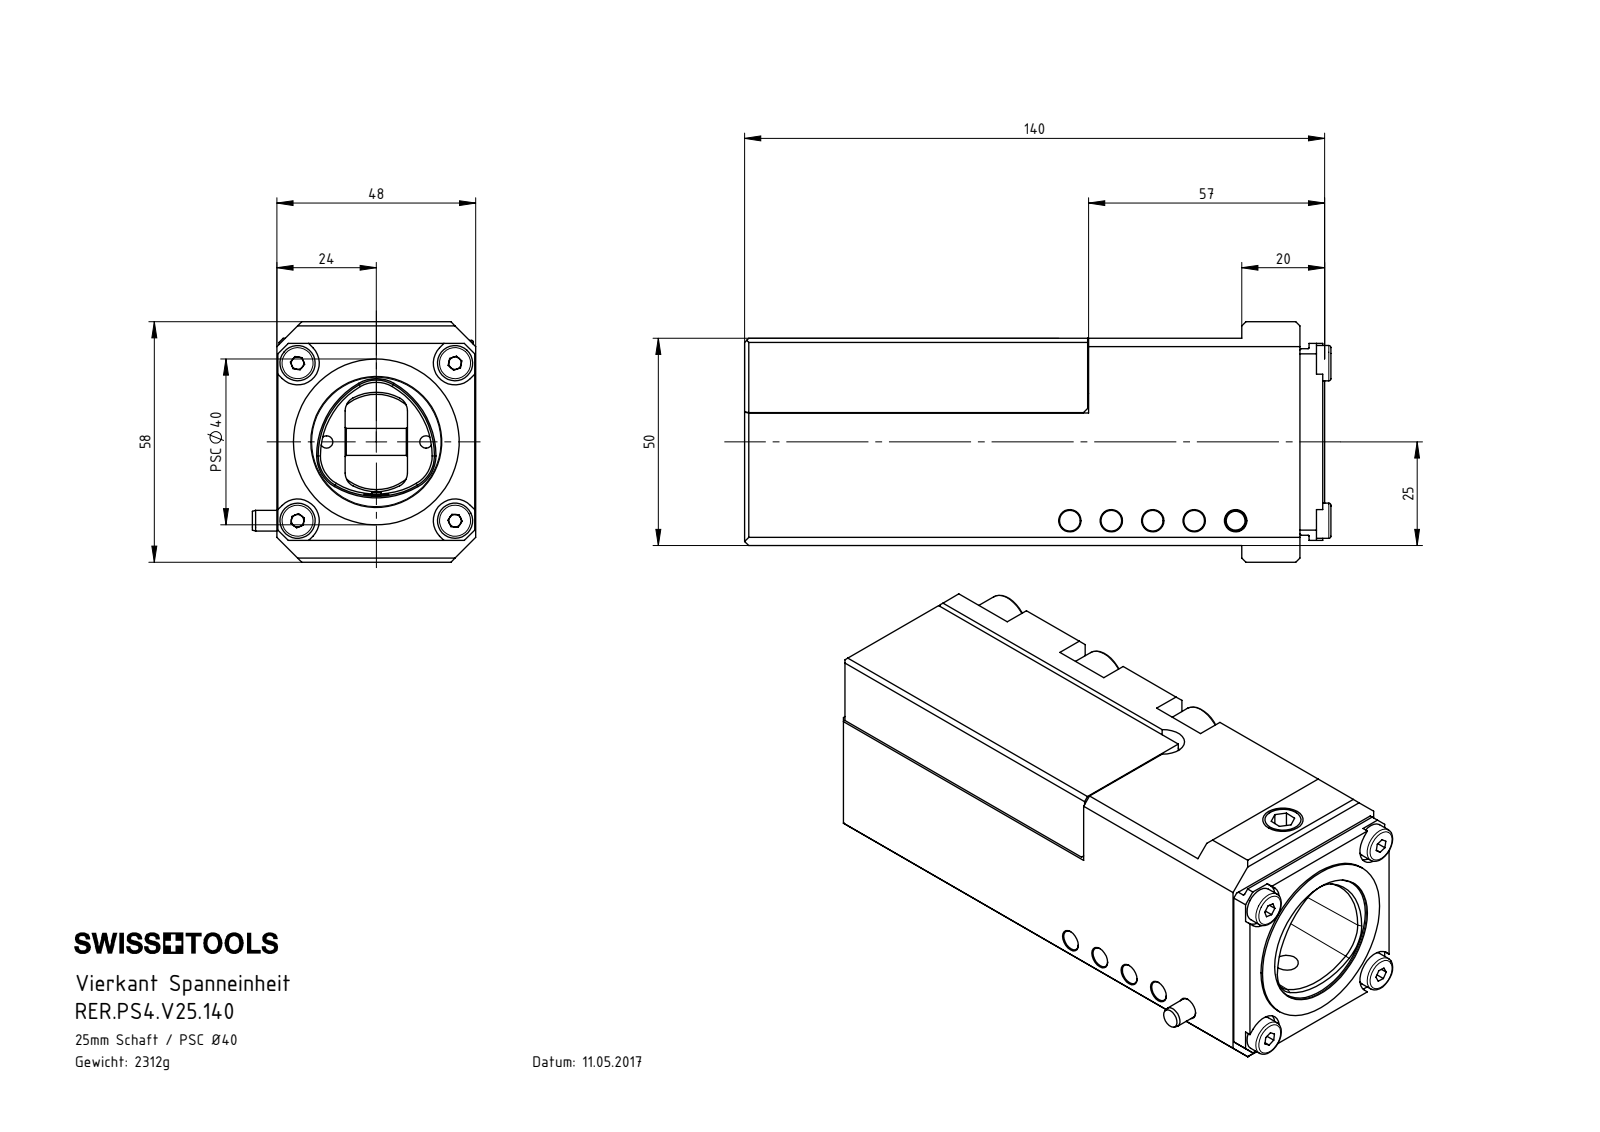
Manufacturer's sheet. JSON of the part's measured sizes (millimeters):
{"part_name": "U40-PS4.ER1.025_B; RER.PS4.V25.140; U40-PS4.ER1.036_A; ISO 8734 - 5 x 16_PreviewCfg (+8 more)", "step_written_by": "SolidWorks 2022 (AUTOMOTIVE_DESIGN)", "units": "millimeters", "bodies": {"solids": 24, "faces": 822, "planar": 341, "cylindrical": 186, "other": 295}, "overall_size": [141.5, 58, 53.92], "volume_mm3": 302394, "surface_area_mm2": 77998, "round_holes": [[5, 5], [4.2, 4], [5.5, 4], [2.5, 3], [6.8, 3], [9, 3], [3, 2], [3.3, 2], [4, 1], [6, 1], [7, 1], [8.57, 1]], "round_bosses_or_shafts": [[8.5, 4], [8, 4], [5, 4], [13, 3], [5.5, 2], [3, 2], [40, 1], [39.7, 1]], "partial_cylinders_radius": [[3.5, 4], [5.25, 4], [7.5, 3], [0.2, 2], [2.75, 2], [3, 2], [9, 1], [12, 1]], "face_to_face_distances": [48, 50, 134, 4, 42, 0.51, 47.49, 47.5, 92, 14], "hole_center_spacings": [10, 20.25, 26.87, 36.36, 38, 20, 12, 12.69]}
